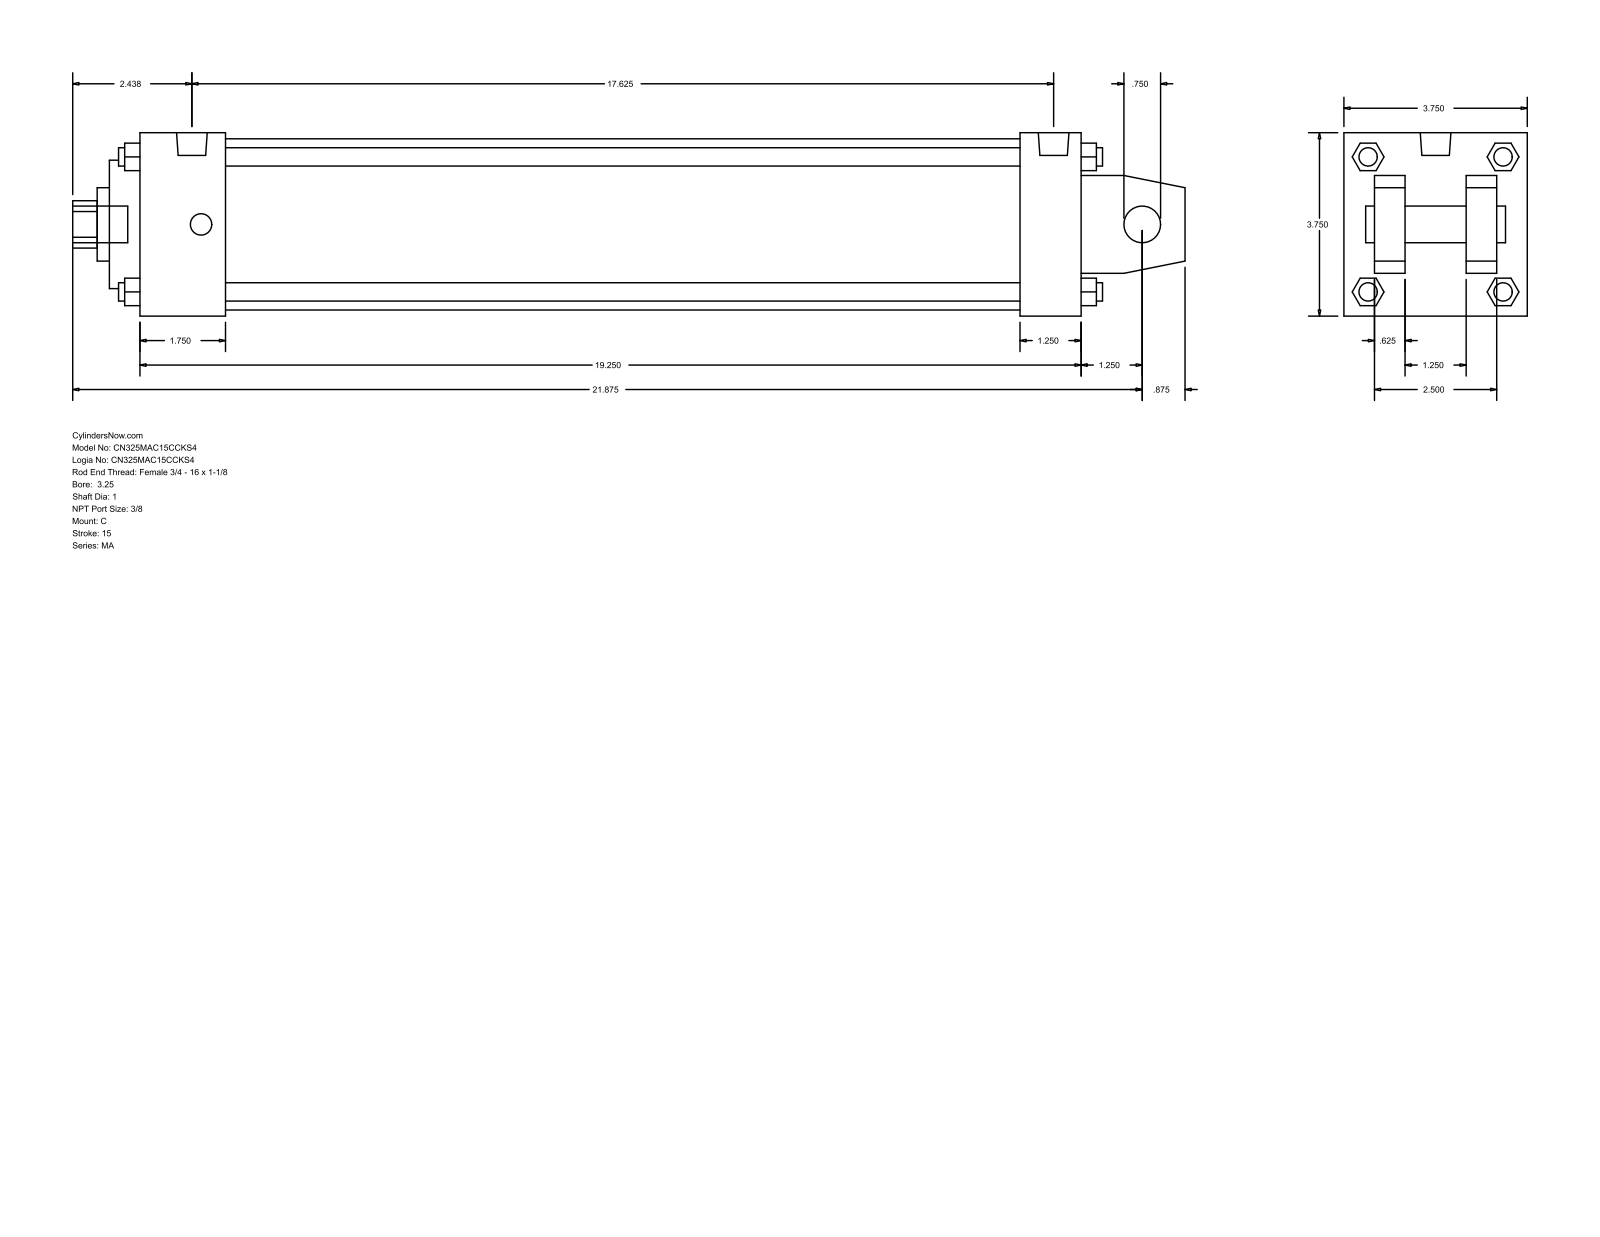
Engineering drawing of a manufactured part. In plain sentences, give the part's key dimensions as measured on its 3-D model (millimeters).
The part is named "MA_C__0325_1". Its 3-D file was written by "GSSL Pune (CONFIG_CONTROL_DESIGN)". It is 0 solids with 141 faces: 109 planar, 32 cylindrical and 0 other. Overall it measures 577.85 by 95.25 by 95.25 millimeters. Round holes: 1 of diameter 19.05, 1 of diameter 25.4, 1 of diameter 38.1, 1 of diameter 66.67, 1 of diameter 88.9. Round bosses or shafts: 4 of diameter 11.11, 4 of diameter 9.53, 2 of diameter 15.93, 1 of diameter 19.05. Partial cylindrical surfaces (rounded edges, fillets, slot ends): 1 of radius 12.29. The main face-to-face distances are 95.24, 15.87, 63.5, 488.96, 31.76, 31.74, 79.37, 47.63, 457.2, 44.46.
